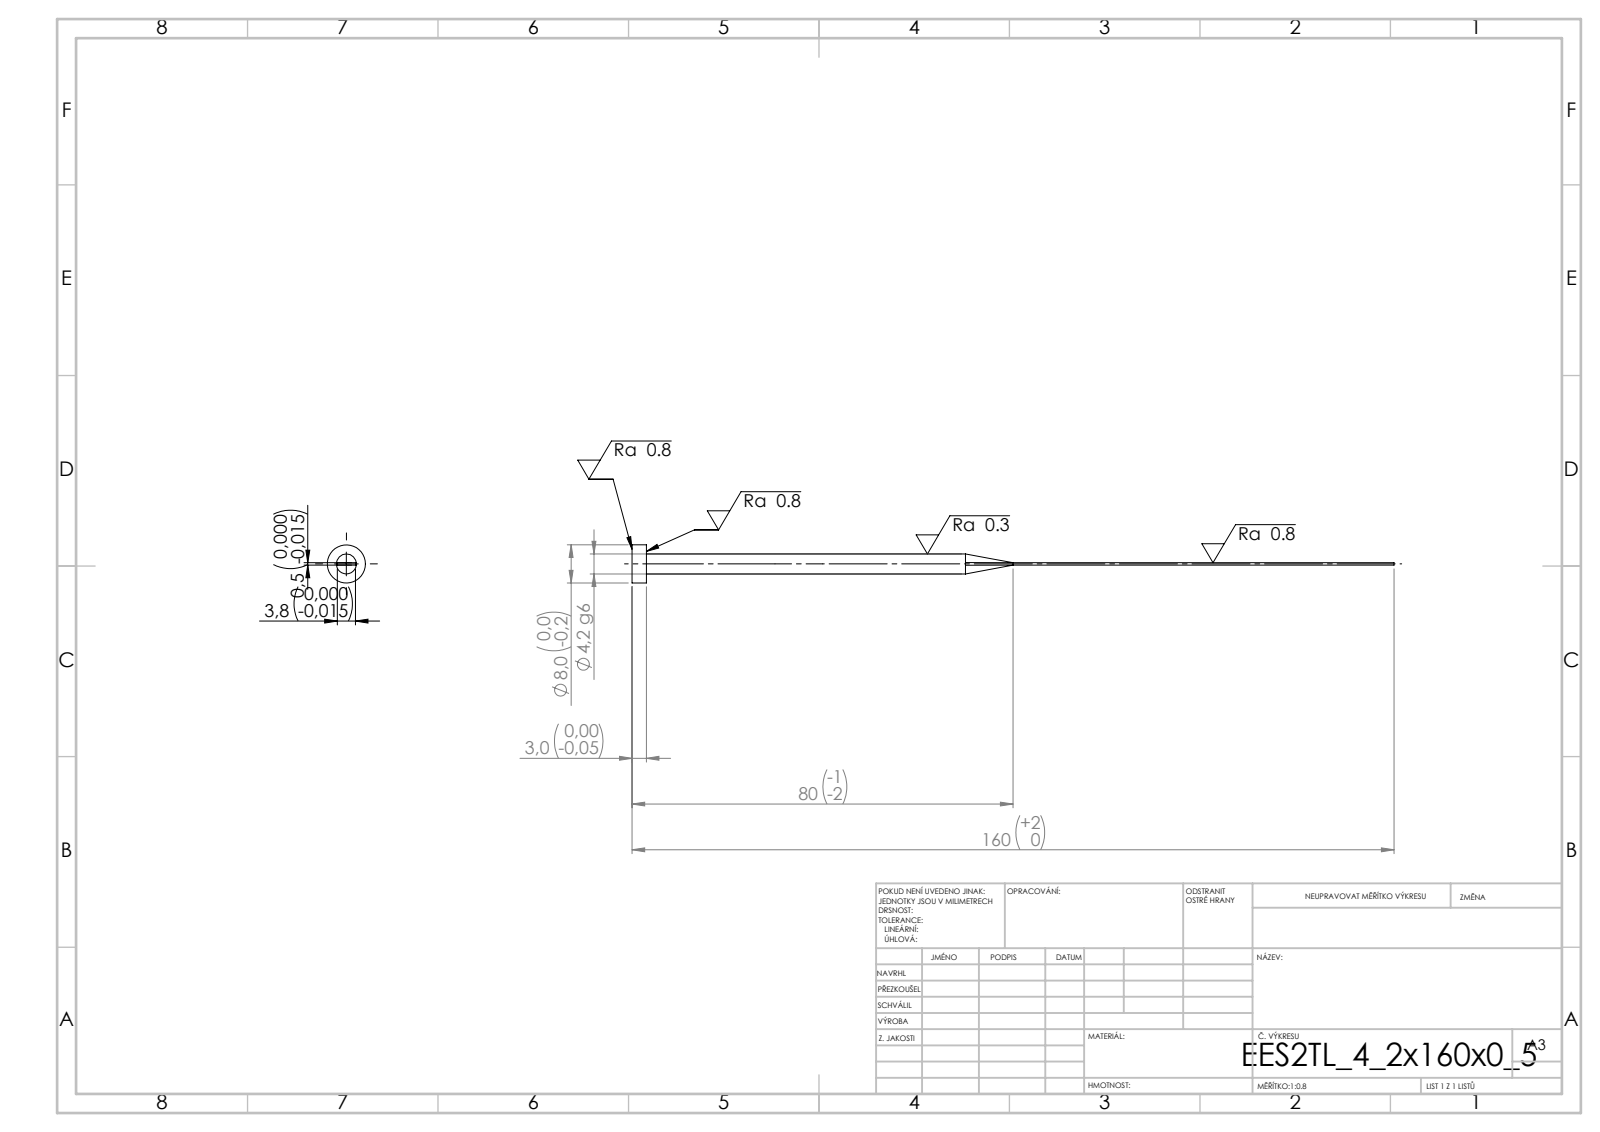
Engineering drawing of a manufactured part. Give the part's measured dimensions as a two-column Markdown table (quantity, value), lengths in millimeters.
| quantity | value |
| --- | --- |
| STEP written by | SolidWorks 2019 (CONFIG_CONTROL_DESIGN) |
| units | millimeters |
| bodies | 1 solid, 15 faces (7 planar, 4 cylindrical, 4 other) |
| overall size | 160 × 8 × 8 |
| volume | 1 304 mm³ |
| surface area | 1 840 mm² |
| round bosses / shafts (diameter × count) | 8 × 1, 4.2 × 1 |
| main face-to-face distances | 0.5, 3.8, 3, 160, 157 |
